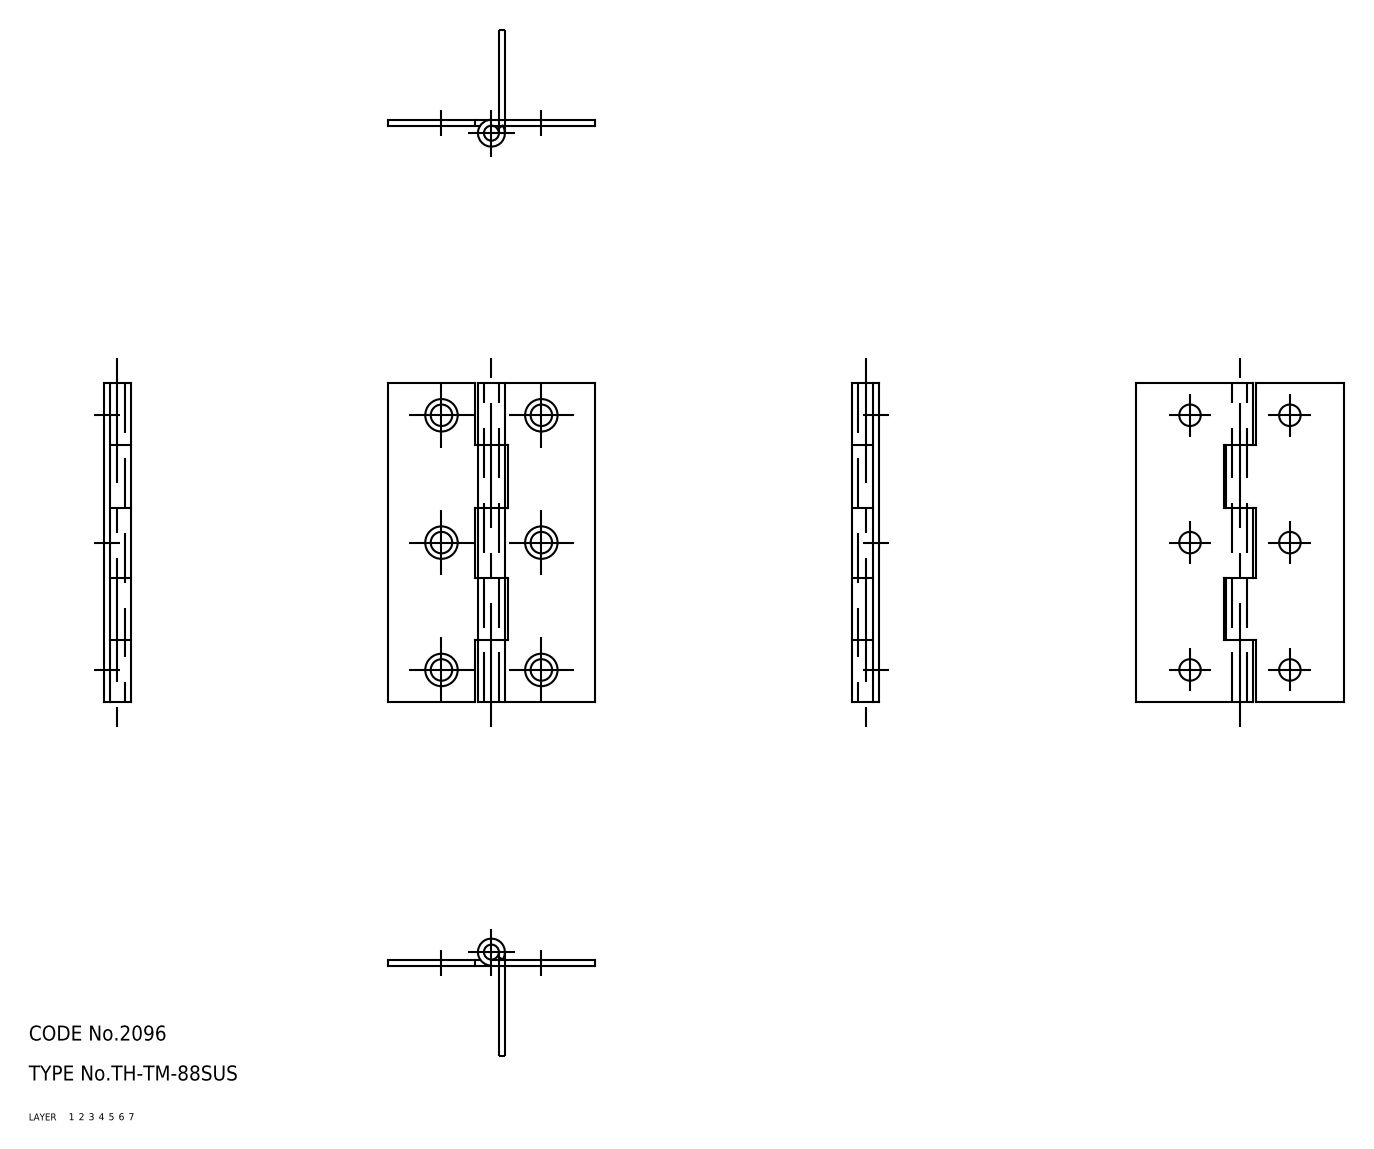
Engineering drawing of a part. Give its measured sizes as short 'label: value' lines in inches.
name: shaft; hinge piece_B; hinge piece_A; TH_TM_88SUS_26520_36
written by: CADfix (AUTOMOTIVE_DESIGN)
unit: in
bodies: 3 solids, 66 faces (0 planar, 0 cylindrical, 66 other)
size: 2.52 × 1.634 × 0.213
volume: 0.249 in³; area: 11.43 in²
